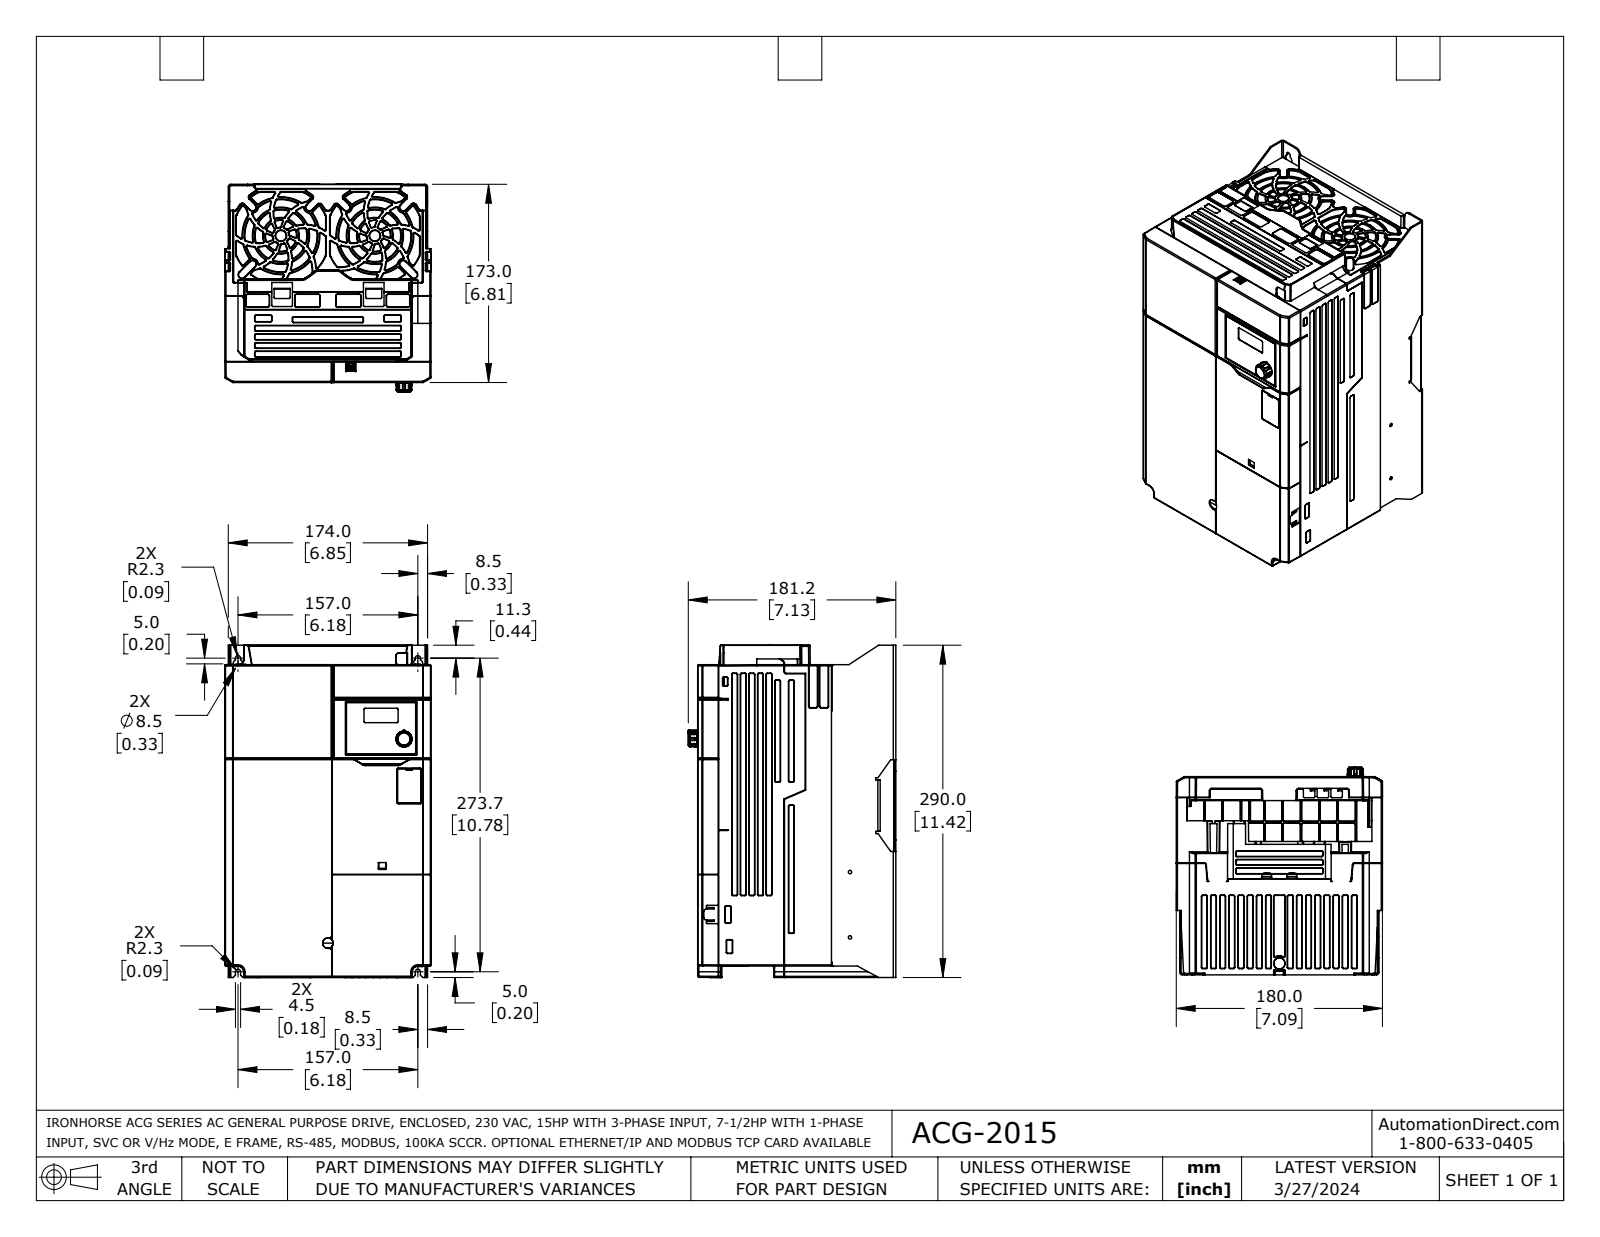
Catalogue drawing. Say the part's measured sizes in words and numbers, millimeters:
The part is named "ACG-2015". Its 3-D file was written by "SolidWorks 2021 (AUTOMOTIVE_DESIGN)". It is 6 solids with 3664 faces: 1665 planar, 663 cylindrical and 1336 other. Overall it measures 290 by 181.2 by 180 millimeters. Its volume is 2 461 000 cubic millimeters and its surface area 552 100 square millimeters. Round holes: 4 of diameter 4.1, 3 of diameter 4.5, 3 of diameter 5.5, 2 of diameter 3, 2 of diameter 8.5, 1 of diameter 1, 1 of diameter 9.2, 1 of diameter 12. Round bosses or shafts: 2 of diameter 9.8, 2 of diameter 8.3, 2 of diameter 5, 1 of diameter 14, 1 of diameter 13.8, 1 of diameter 8.5, 1 of diameter 8, 1 of diameter 6.6. Partial cylindrical surfaces (rounded edges, fillets, slot ends): 124 of radius 1, 108 of radius 0.2, 95 of radius 0.5, 36 of radius 0.3, 14 of radius 2, 12 of radius 5, 9 of radius 2.2, 6 of radius 4.5. The main face-to-face distances are 1.4, 173, 171.6, 11.5, 168.5, 157, 3, 177, 8.5, 165.5. The hole center spacings are 11, 22.7, 24, 35, 46, 46.6, 57.6, 68.6.
